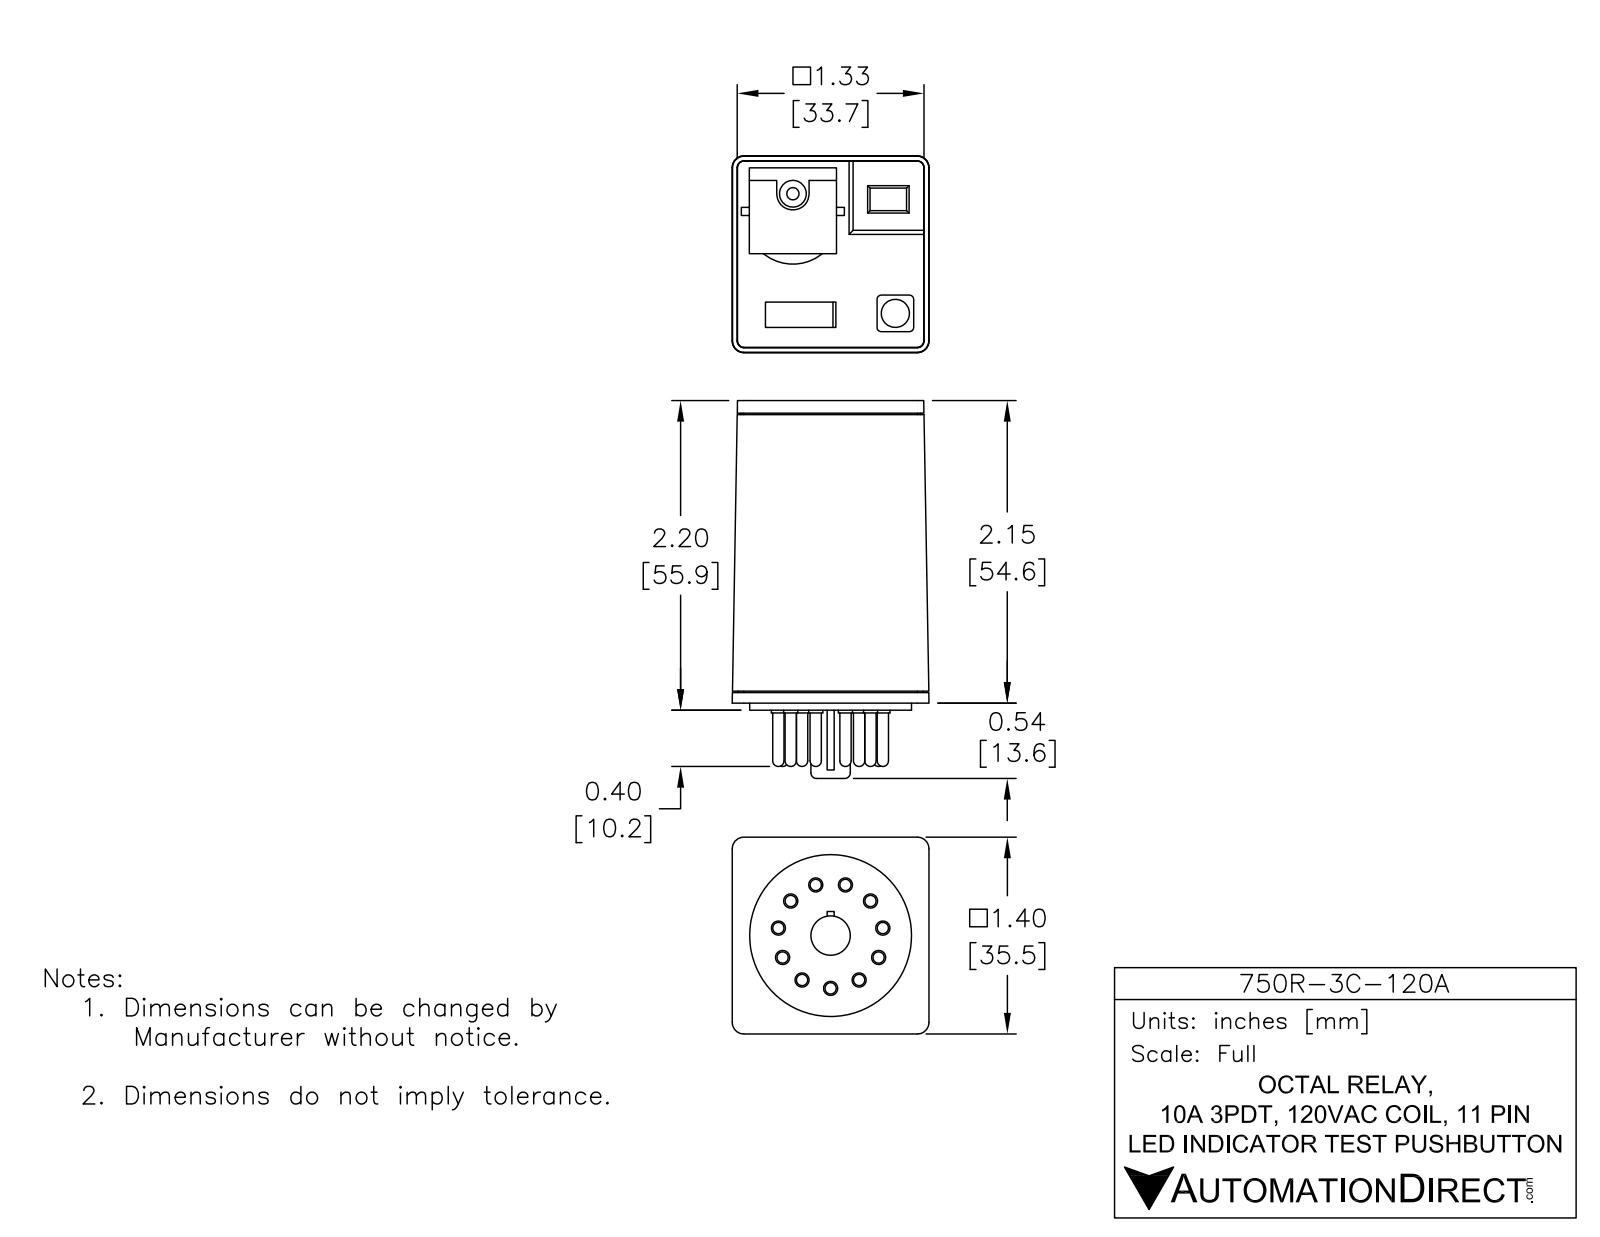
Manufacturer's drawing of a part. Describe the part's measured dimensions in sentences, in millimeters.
The part is named "750R-3C-120A". Its 3-D file was written by "SolidWorks 2014 (AUTOMOTIVE_DESIGN)". It is 1 solid with 180 faces: 93 planar, 62 cylindrical and 25 other. Overall it measures 68.2 by 35.5 by 35.5 millimeters. Its volume is 66 470 cubic millimeters and its surface area 11 410 square millimeters. Round holes: 1 of diameter 2.2, 1 of diameter 5.1. Round bosses or shafts: 11 of diameter 2.5, 11 of diameter 2, 1 of diameter 29.2, 1 of diameter 7.1, 1 of diameter 4.8. Partial cylindrical surfaces (rounded edges, fillets, slot ends): 4 of radius 0.8, 1 of radius 2.9, 1 of radius 8.4. The main face-to-face distances are 1.3, 54.6, 55.9, 53.6, 1, 55.6, 54.4, 2.2, 0.8, 54.9. The hole center spacings are 28.4.
